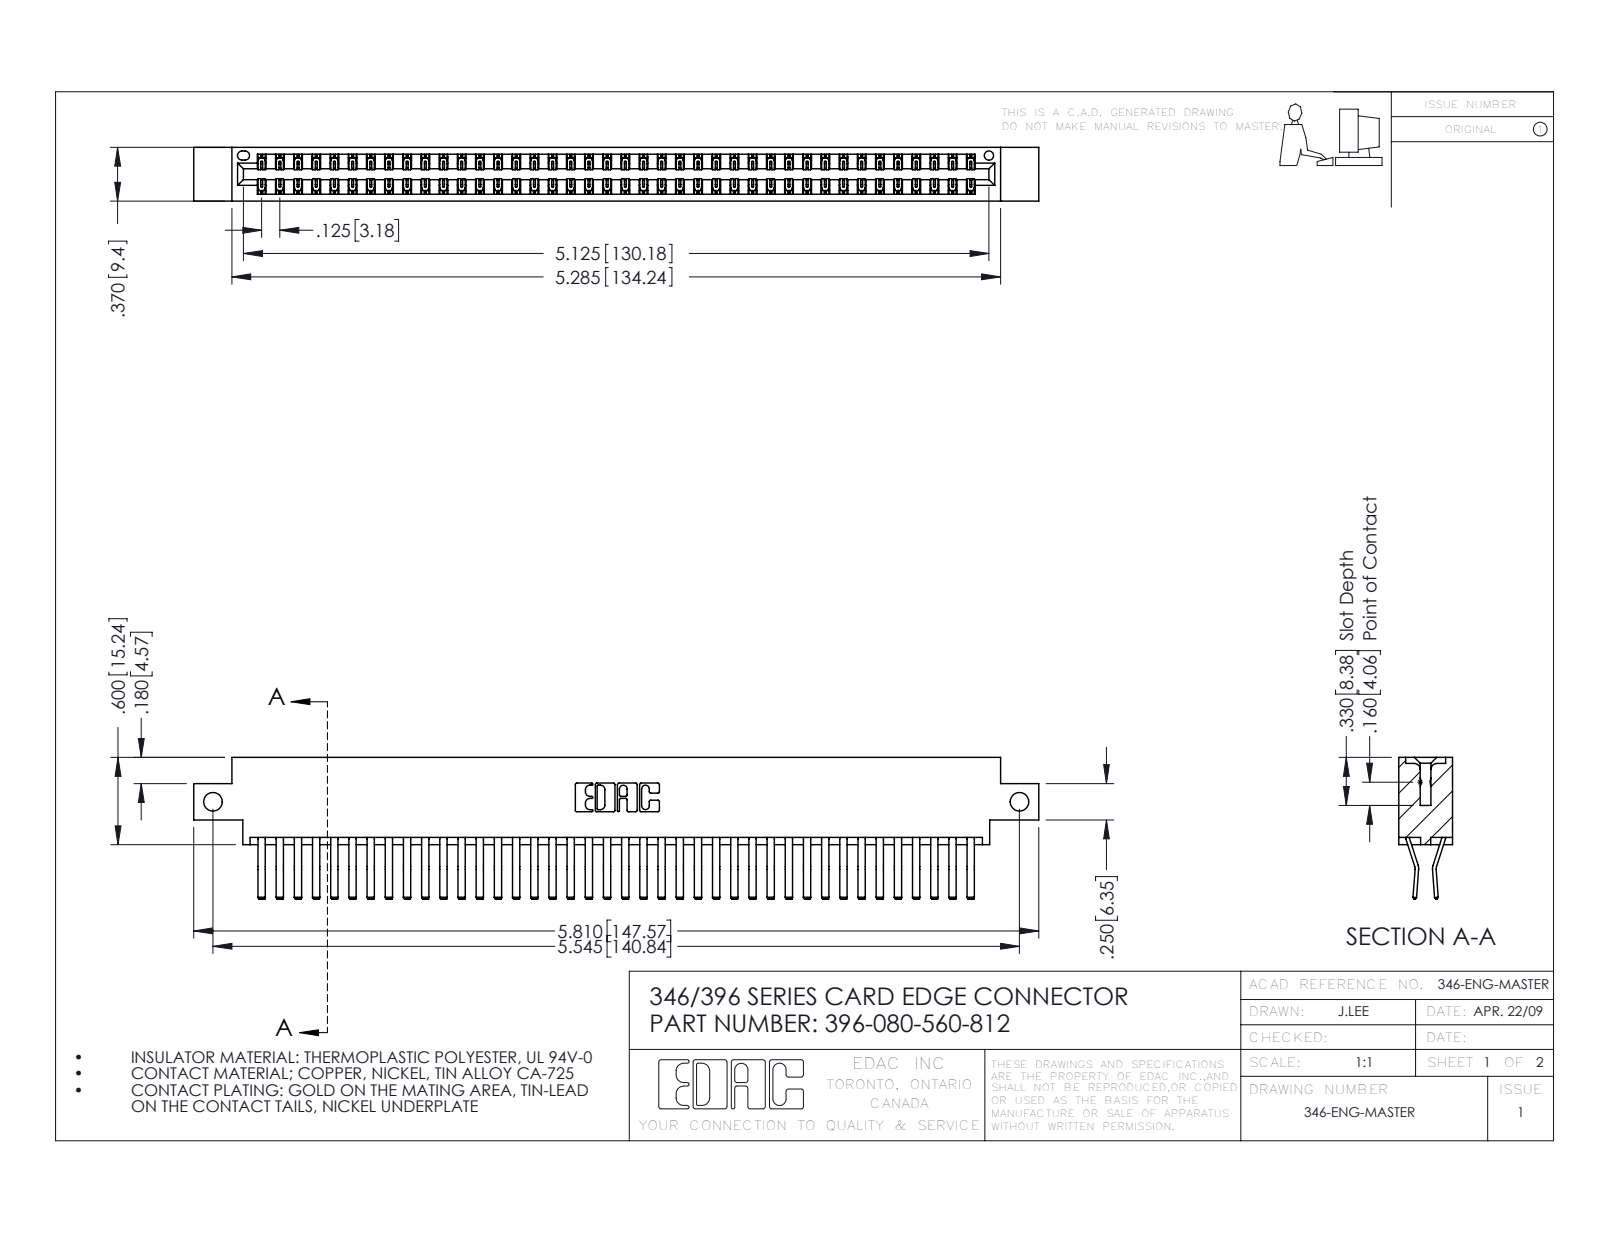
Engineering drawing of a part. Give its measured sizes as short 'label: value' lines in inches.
name: 396-080-560-812; 345-292-001_560 Tail; 346 Part_0.170 Offset - Side Mount
written by: SolidWorks 2016 (CONFIG_CONTROL_DESIGN)
unit: in
bodies: 81 solids, 4446 faces (2880 planar, 1566 cylindrical, 0 other)
size: 5.81 × 0.975 × 0.37
volume: 0.894 in³; area: 33.41 in²
holes: 2× ⌀0.128, 1× ⌀0.064
rounds: 120× R0.006, 22× R0.01, 6× R0.007, 6× R0.031, 3× R0.026, 2× R0.01, 2× R0.014, 2× R0.022
face distances: 0.048, 0.322, 0.37, 0.025, 0.25, 0.072, 0.298, 0.275, 0.148, 0.222
hole spacings: 5.545
